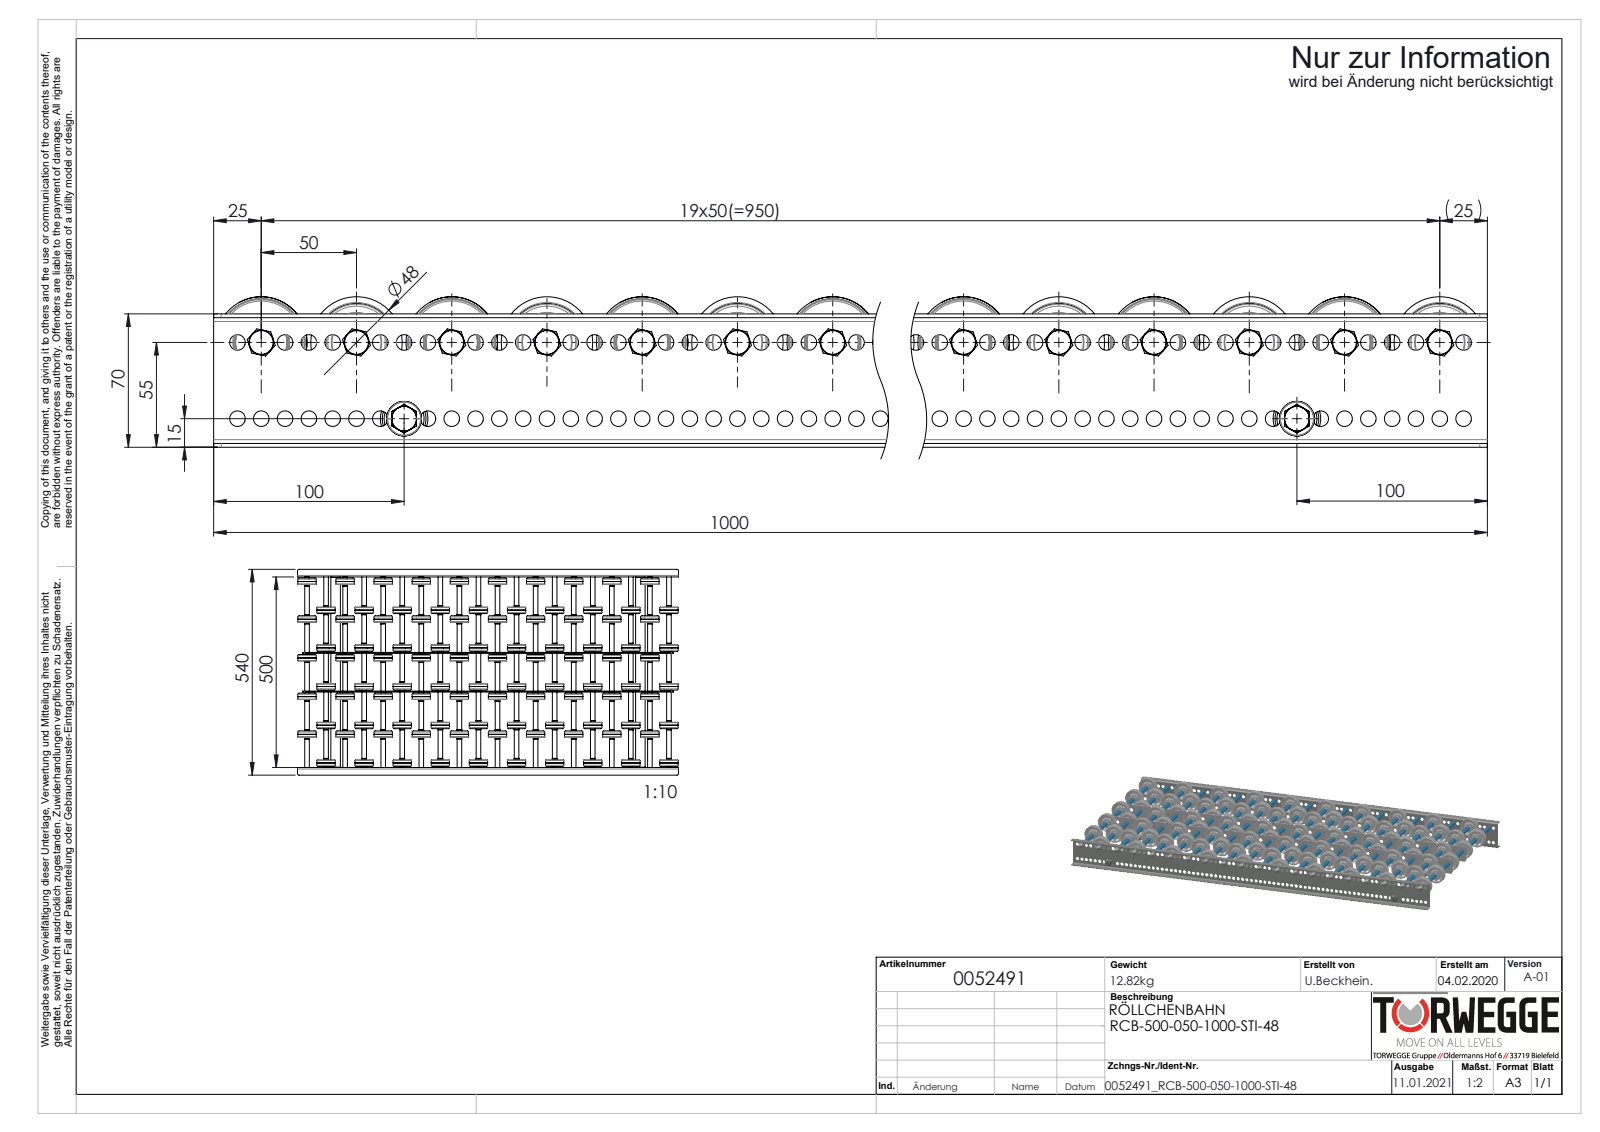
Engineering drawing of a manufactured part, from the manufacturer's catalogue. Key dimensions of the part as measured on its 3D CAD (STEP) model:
Part name (STEP PRODUCT): 0046278_KB-ROHR-12X1,75mm_KFG_L75; Profil_LRB-20x70x20x2_KFG_S100200_U-PROFIL-20-70-20-2-LRB-L=1000; S100100_Längstraverse-42x2,5_S100147_Lngstraverse-RB-1000; K0011528_2200-48-8 (+6 more)
STEP written by: SolidWorks 2020 (AUTOMOTIVE_DESIGN)
Units: millimetres
Bodies: 374 solids, 10968 faces (2292 planar, 4052 cylindrical, 4624 other)
Overall size (bounding box): 1000 × 540 × 79
Volume: 3 707 000 mm³ · Surface area: 2 776 000 mm²
Round holes (diameter × count): ⌀8.2 ×158, ⌀8.5 ×39, ⌀6.65 ×20, ⌀8 ×20, ⌀9.65 ×20, ⌀15 ×20, ⌀41 ×20, ⌀6.8 ×2, ⌀21 ×2
Round bosses / shafts (diameter × count): ⌀48 ×20, ⌀13 ×20, ⌀12.5 ×20, ⌀12.4 ×20, ⌀12 ×20, ⌀11.5 ×20, ⌀25 ×2, ⌀8 ×2
Partial cylindrical surfaces — rounded edges, fillets, slot ends (radius × count): R4 ×8, R2 ×4, R5 ×4
Main face-to-face distances: 200.5, 302, 101.5, 12, 87, 99, 75, 2, 186, 188.5
Hole centre spacings: 12.5, 25, 37.5, 50, 62.5, 75, 87.5, 100
